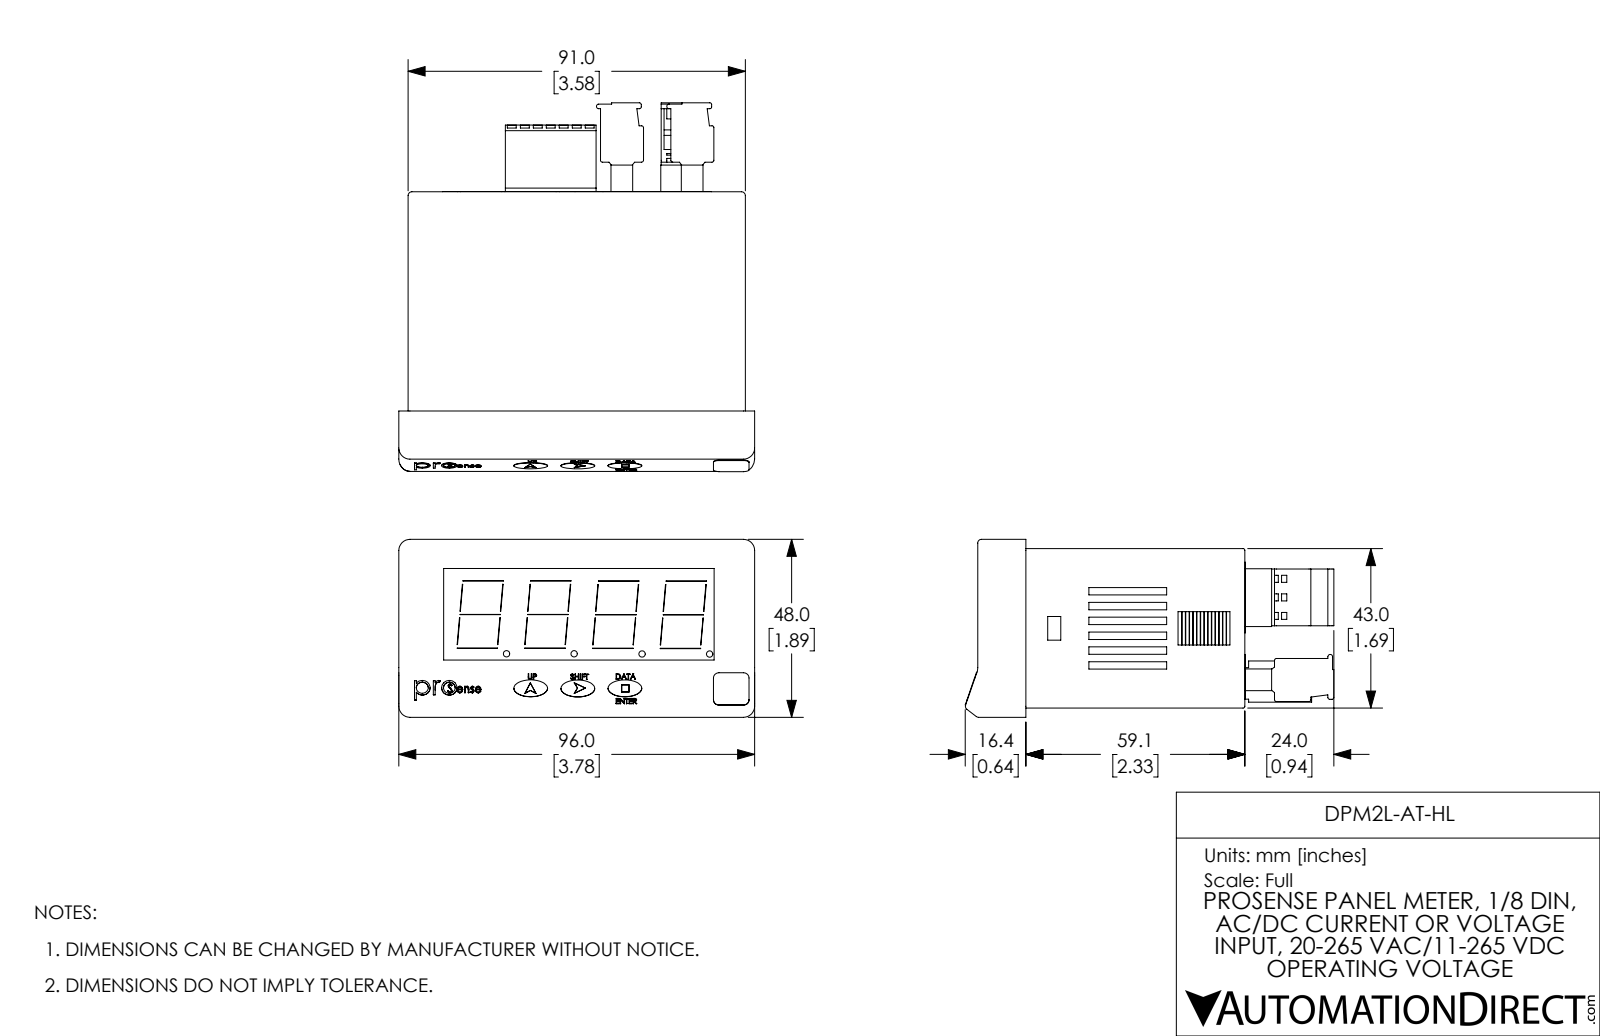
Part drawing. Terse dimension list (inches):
name: DPM2L-AT-HL
written by: SolidWorks 2017 (AUTOMOTIVE_DESIGN)
unit: in
bodies: 9 solids, 1824 faces (1410 planar, 258 cylindrical, 156 other)
size: 3.916 × 3.78 × 1.89
volume: 5.302 in³; area: 98.06 in²
holes: 8× ⌀0.078, 8× ⌀0.118, 8× ⌀0.152, 7× ⌀0.039, 7× ⌀0.079
bosses: 4× ⌀0.068
rounds: 53× R0.004, 17× R0.02, 14× R0.012, 14× R0.014, 10× R0.118, 9× R0.039, 8× R0.121, 7× R0.07
face distances: 0.059, 1.634, 0.098, 1.693, 1.575, 1.732, 3.524, 0.433, 0.157, 2.78
hole spacings: 0.138, 0.748, 0.197, 0.197, 0.201, 0.201, 0.276, 0.398
